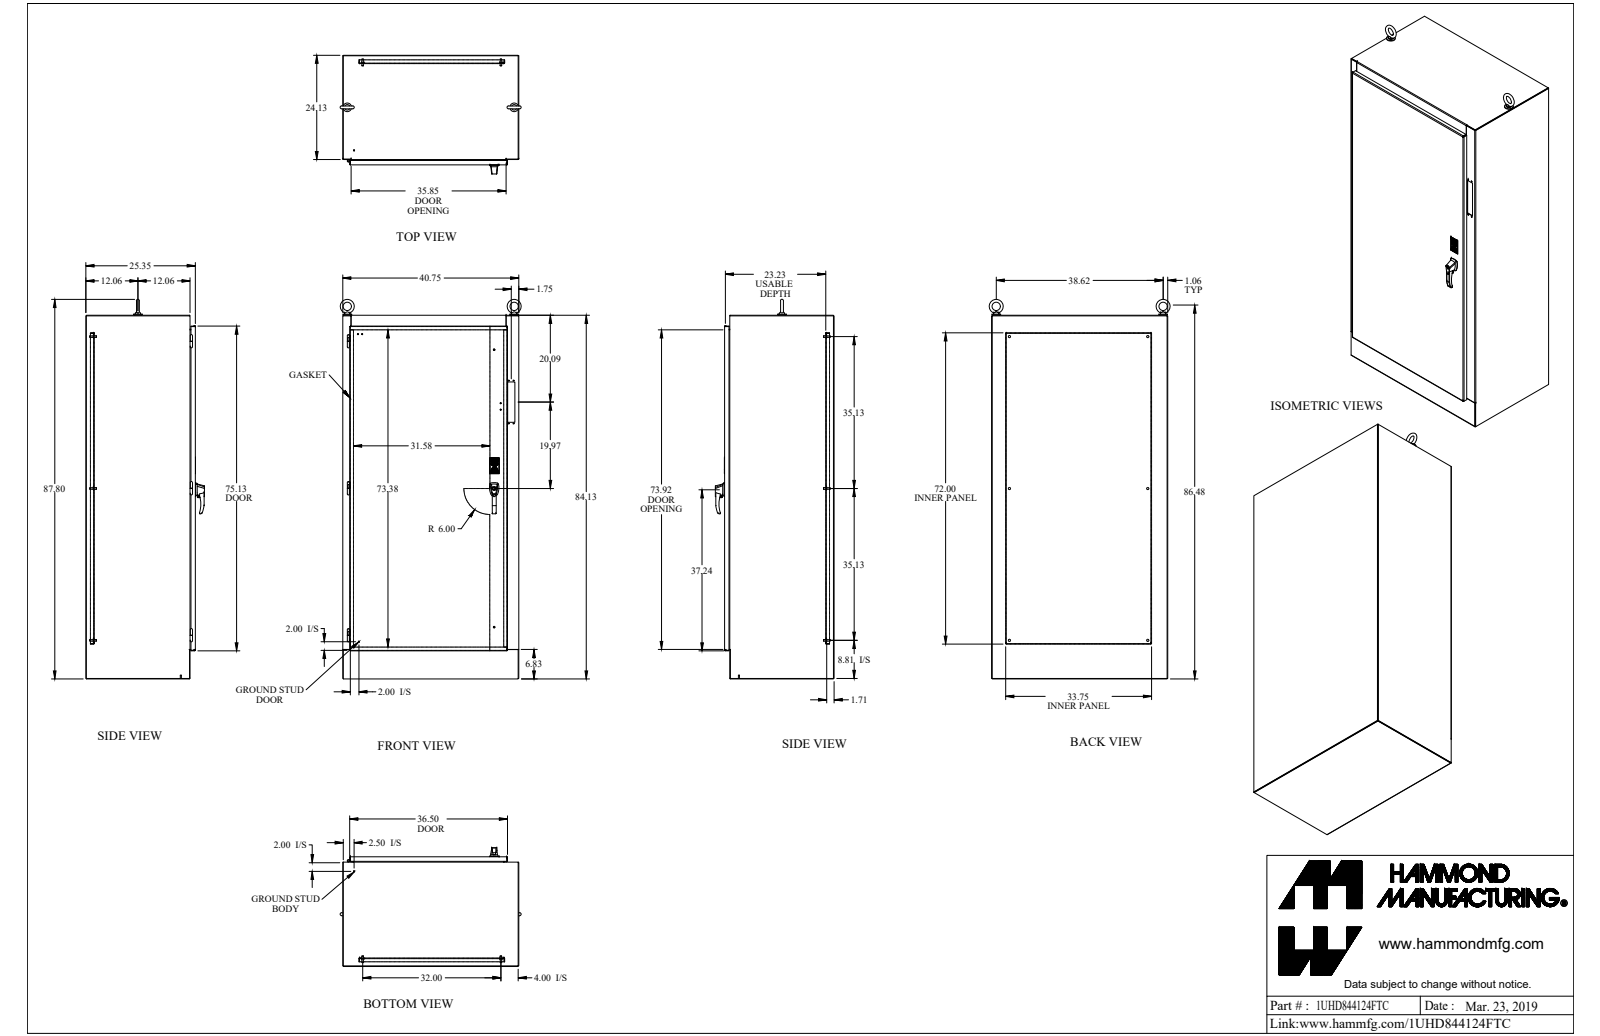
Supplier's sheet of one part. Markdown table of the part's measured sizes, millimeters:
| quantity | value |
| --- | --- |
| part name | 1UHD844124FTC |
| STEP written by | SolidWorks 2018 (AUTOMOTIVE_DESIGN) |
| units | millimeters |
| bodies | 102 solids, 1773 faces (978 planar, 482 cylindrical, 313 other) |
| overall size | 2230.1 × 1063.5 × 697.6 |
| volume | 36 020 000 mm³ |
| surface area | 22 720 000 mm² |
| round holes (diameter × count) | 7.8 × 7, 8.9 × 7, 7.1 × 6, 11.3 × 6, 14.3 × 6, 5 × 5, 6.4 × 3, 8 × 3, 4.2 × 2, 6.5 × 2, 6.5 × 2, 7.1 × 2 |
| round bosses / shafts (diameter × count) | 6.4 × 10, 25.4 × 8, 9.5 × 7, 16.5 × 6, 8.4 × 6, 7.1 × 4, 4.8 × 4, 15.9 × 3 |
| partial cylindrical surfaces (radius × count) | 1.5 × 39, 4.7 × 28, 12.7 × 25, 3.2 × 22, 0.4 × 16, 0.8 × 12, 3.3 × 8, 19.1 × 7 |
| main face-to-face distances | 3.2, 640.7, 3.2, 637.5, 643.9, 49.2, 46, 591.5, 594.7, 46 |
| hole center spacings | 812.8, 25.4, 28.6, 28.6, 32.7, 50.8, 188.8, 189.6 |
